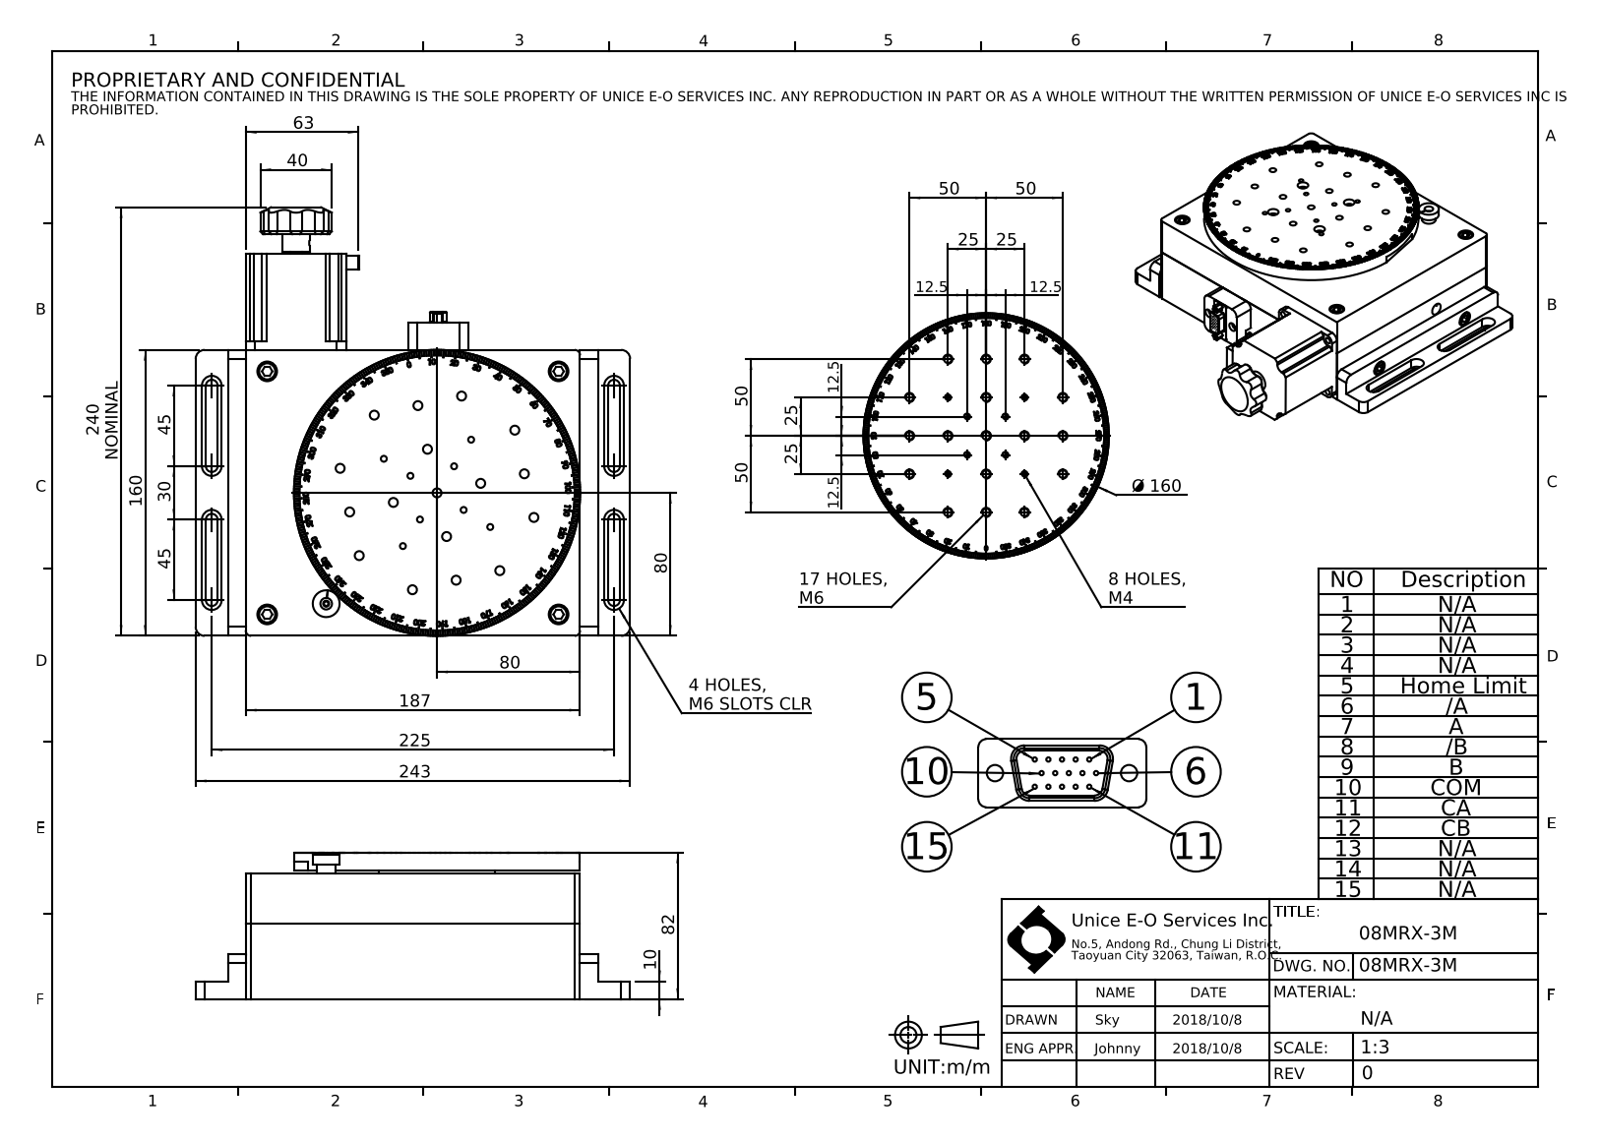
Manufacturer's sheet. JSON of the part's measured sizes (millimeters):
{"part_name": "08MRX-3M", "step_written_by": "SolidWorks 2016 (AUTOMOTIVE_DESIGN)", "units": "millimeters", "bodies": {"solids": 0, "faces": 1075, "planar": 737, "cylindrical": 264, "other": 74}, "overall_size": [243, 239.8, 82], "round_holes": [[5, 19], [0.8, 14], [4.5, 12], [3.3, 8], [11, 6], [8, 4], [8.6, 4], [6.5, 3], [1, 2], [2.5, 2], [3.4, 2], [9, 1]], "round_bosses_or_shafts": [[10, 4], [15, 2], [160, 1], [84, 1]], "partial_cylinders_radius": [[5, 14], [3.3, 8], [4, 8], [5.5, 8], [7, 8], [0.5, 7], [2, 4], [4.5, 4]], "face_to_face_distances": [10, 70.5, 42, 28.5, 72, 82, 40, 11.5, 1.5, 30], "hole_center_spacings": [55.9, 25, 79.06, 17.68, 35.36, 2.84, 39.52, 39.53]}
